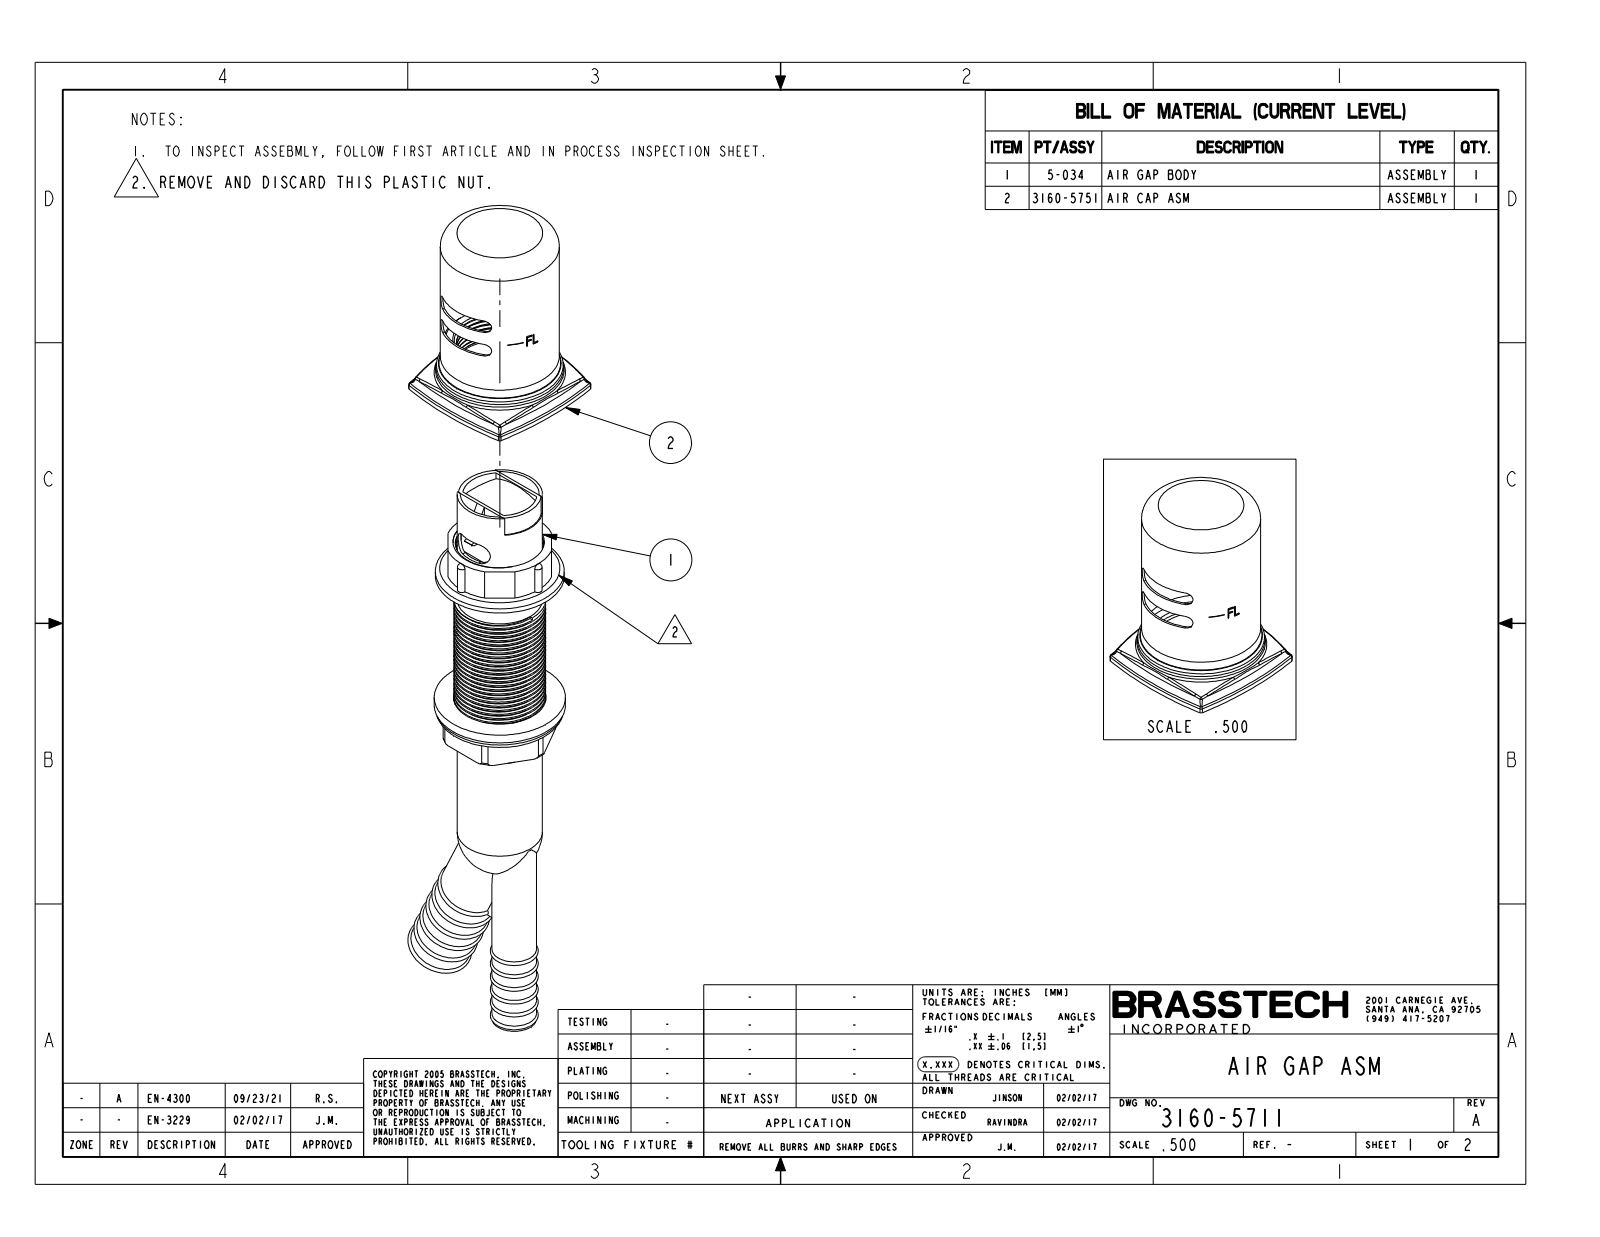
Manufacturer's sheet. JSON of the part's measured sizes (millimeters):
{"part_name": "3160-5711", "step_written_by": "CREO PARAMETRIC BY PTC INC, 2018400 (AUTOMOTIVE_DESIGN)", "units": "millimeters", "bodies": {"solids": 2, "faces": 331, "planar": 66, "cylindrical": 138, "other": 127}, "overall_size": [223.6, 64.7, 49], "volume_mm3": 165700, "surface_area_mm2": 51660, "round_holes": [[30.5, 1], [32.3, 1], [32.5, 1], [40, 1]], "round_bosses_or_shafts": [[45.7, 1], [44.7, 1], [41.5, 1], [32, 1], [29.7, 1], [21.7, 1], [15.5, 1]], "partial_cylinders_radius": [[1, 6], [0.8, 4], [2.5, 4], [131.6, 4], [133.4, 4], [4, 2], [20.5, 1]], "face_to_face_distances": [23.4, 89, 89.8, 65.7, 66.4, 0.8, 34.2, 10.8, 54.9, 55.6]}
